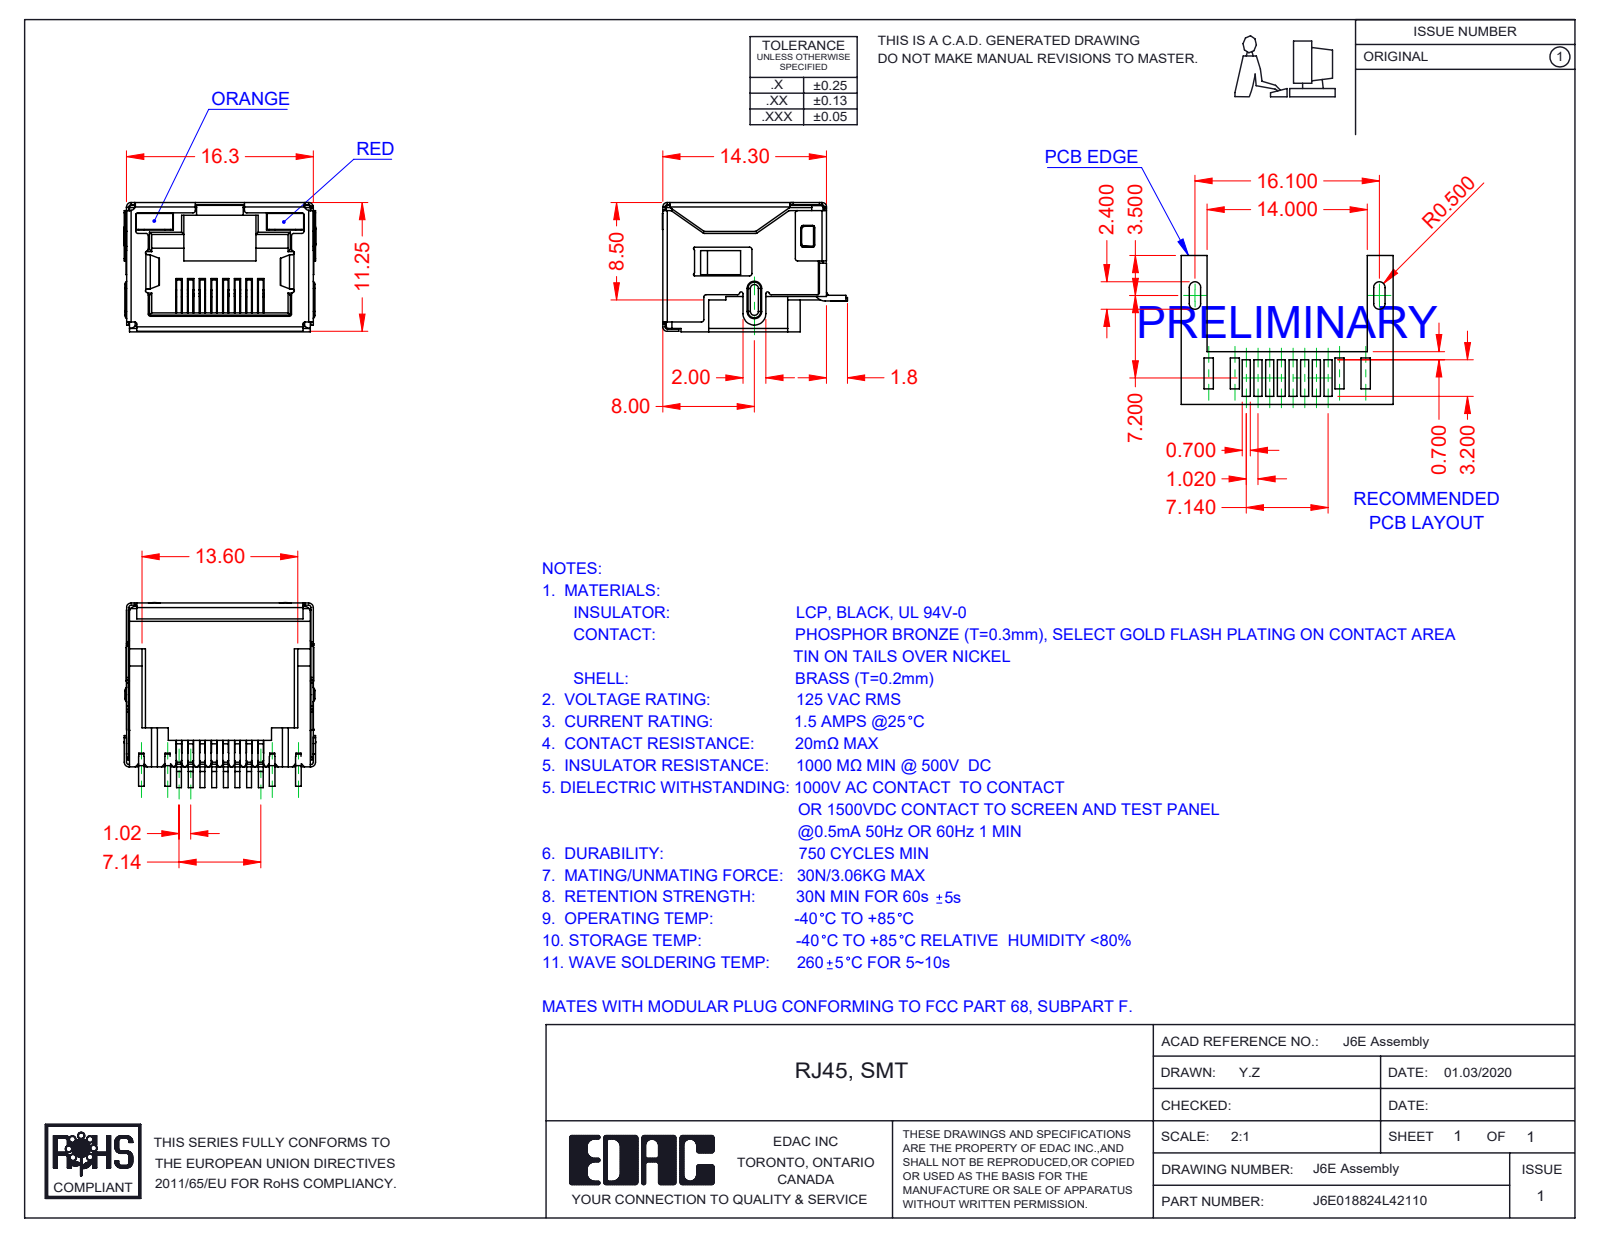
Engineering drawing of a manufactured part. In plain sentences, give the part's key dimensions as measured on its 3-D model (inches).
The part is named "6E LED LH_4-Orange; 6E Insulator_LED; J6E018824L42110; 6E LED RH_2-Red (+2 more)". Its 3-D file was written by "SolidWorks 2016 (CONFIG_CONTROL_DESIGN)". It is 12 solids with 1496 faces: 1099 planar, 347 cylindrical and 50 other. Overall it measures 0.659 by 0.636 by 0.445 inches. Its volume is 0.068 cubic inches and its surface area 6.27 square inches. Partial cylindrical surfaces (rounded edges, fillets, slot ends): 82 of radius 0.008, 17 of radius 0.01, 13 of radius 0.016, 13 of radius 0.02, 10 of radius 0.004, 7 of radius 0.006, 4 of radius 0.012, 3 of radius 0.039. The main face-to-face distances are 0.435, 0.632, 0.634, 0.624, 0.437, 0.445, 0.094, 0.028, 0.388, 0.019.
